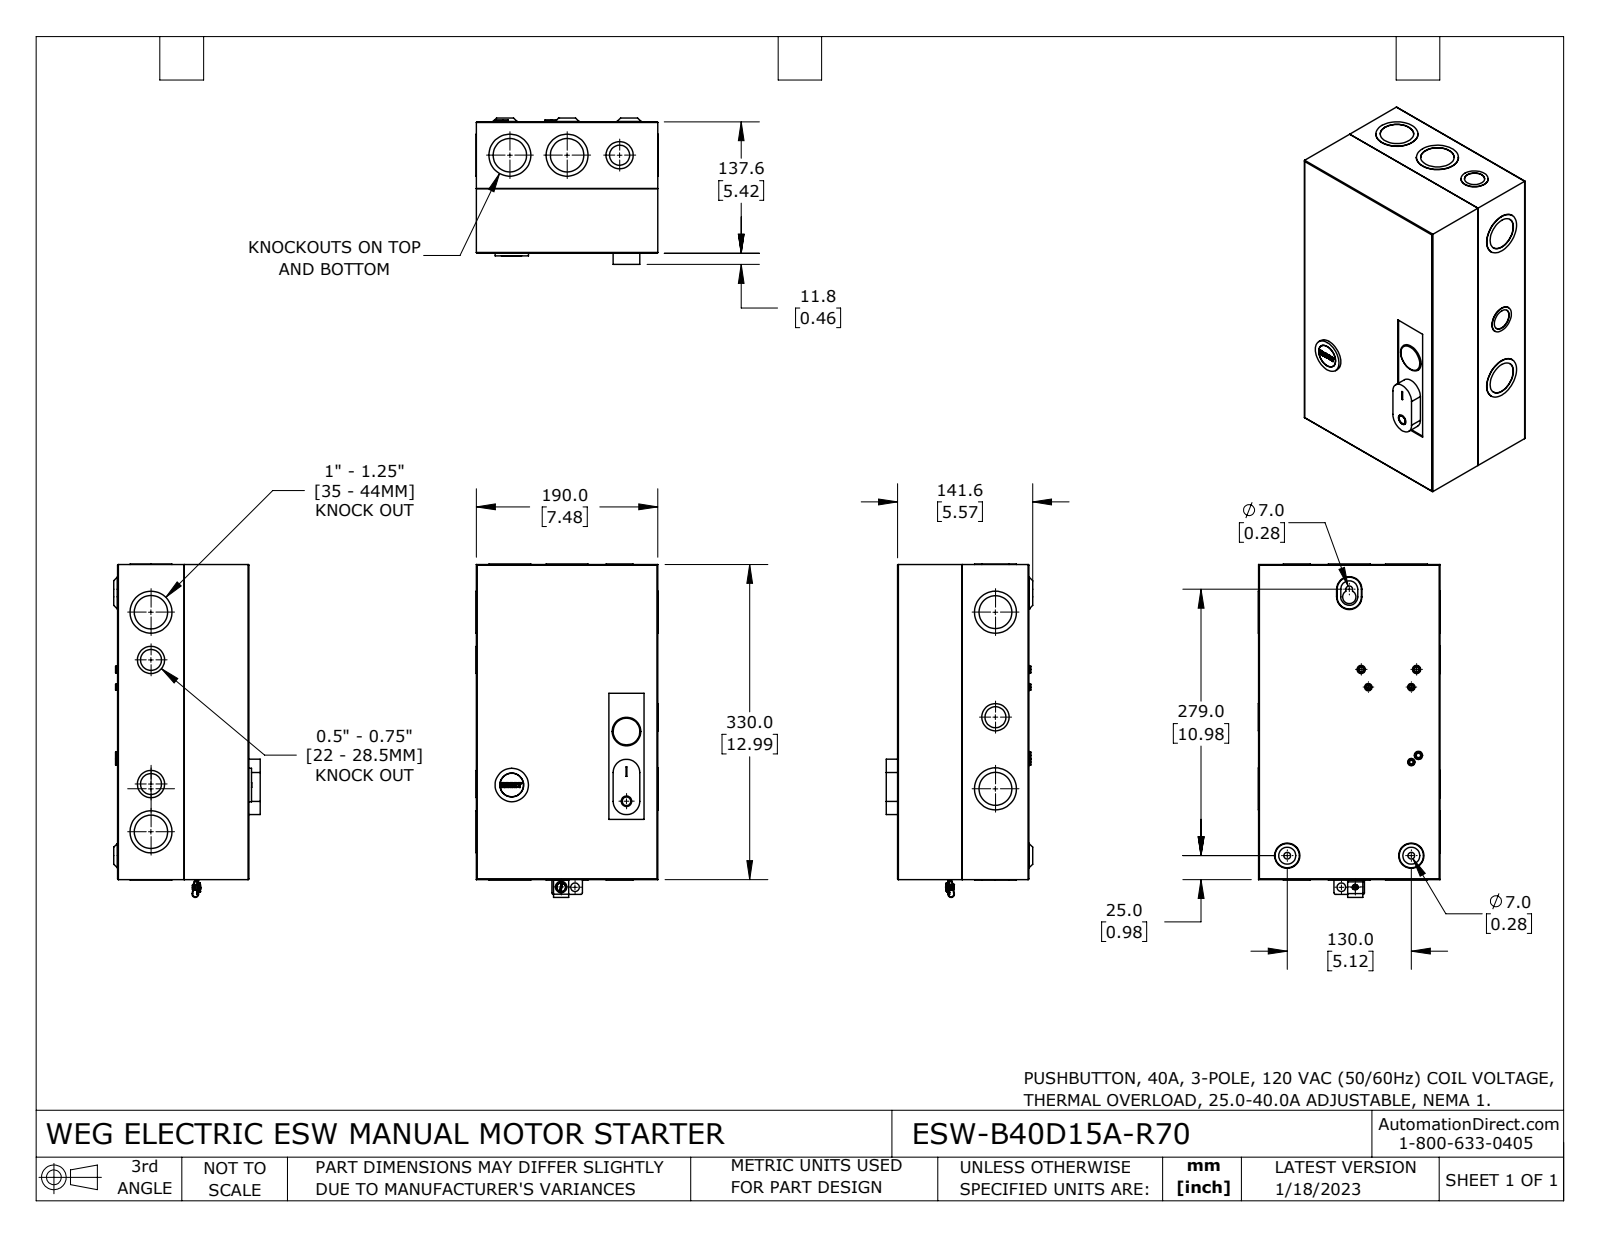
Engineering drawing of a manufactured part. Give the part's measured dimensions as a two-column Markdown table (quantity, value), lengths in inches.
| quantity | value |
| --- | --- |
| part name | ESW-B40D15A-R70 |
| STEP written by | SolidWorks 2021 (CONFIG_CONTROL_DESIGN) |
| units | inches |
| bodies | 7 solids, 435 faces (161 planar, 221 cylindrical, 53 other) |
| overall size | 13.74 × 7.504 × 6.039 |
| volume | 24.58 in³ |
| surface area | 936.7 in² |
| round holes (diameter × count) | 1.378 × 4, 0.146 × 3, 0.183 × 3, 0.276 × 2, 0.866 × 2, 0.886 × 2, 1.357 × 2, 0.256 × 1, 0.279 × 1, 0.354 × 1, 0.433 × 1, 0.469 × 1 |
| round bosses / shafts (diameter × count) | 1.732 × 4, 1.122 × 3, 0.278 × 3, 0.24 × 3, 1.734 × 2, 1.378 × 1, 1.193 × 1, 1.148 × 1 |
| partial cylindrical surfaces (radius × count) | 0.004 × 34, 0.031 × 8, 0.079 × 3, 0.138 × 3, 0.059 × 2, 0.075 × 2, 0.108 × 2, 0.122 × 2 |
| main face-to-face distances | 0.047, 5.37, 7.433, 5.323, 5.417, 12.945, 7.386, 7.48, 0.071, 12.898 |
| hole center spacings | 0.571, 1.772, 1.969, 2.283, 2.362, 5.118, 7.087, 10.972 |
